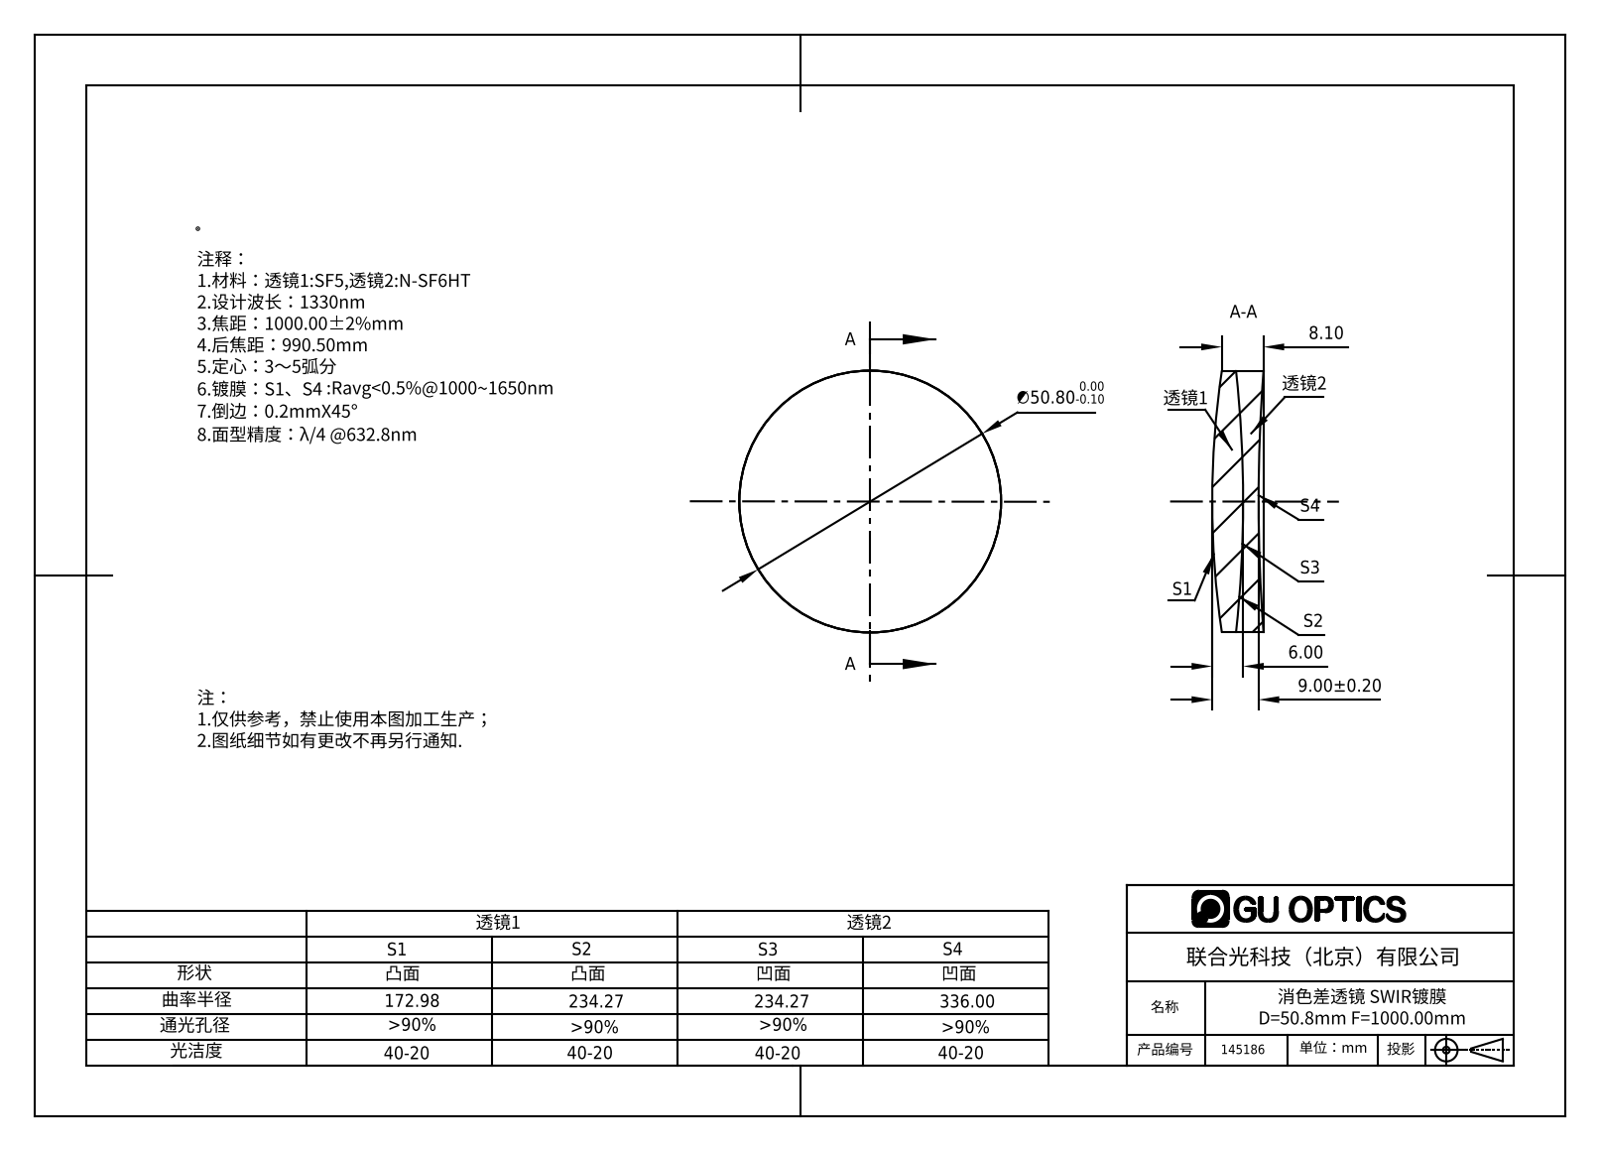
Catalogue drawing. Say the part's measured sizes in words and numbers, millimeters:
The part is named "145186". Its 3-D file was written by "SolidWorks 2016 (AUTOMOTIVE_DESIGN)". It is 2 solids with 12 faces: 0 planar, 4 cylindrical and 8 other. Overall it measures 50.8 by 50.8 by 9.96 millimeters. Its volume is 17 319 cubic millimeters and its surface area 9 424 square millimeters. Round bosses or shafts: 1 of diameter 50.8.
